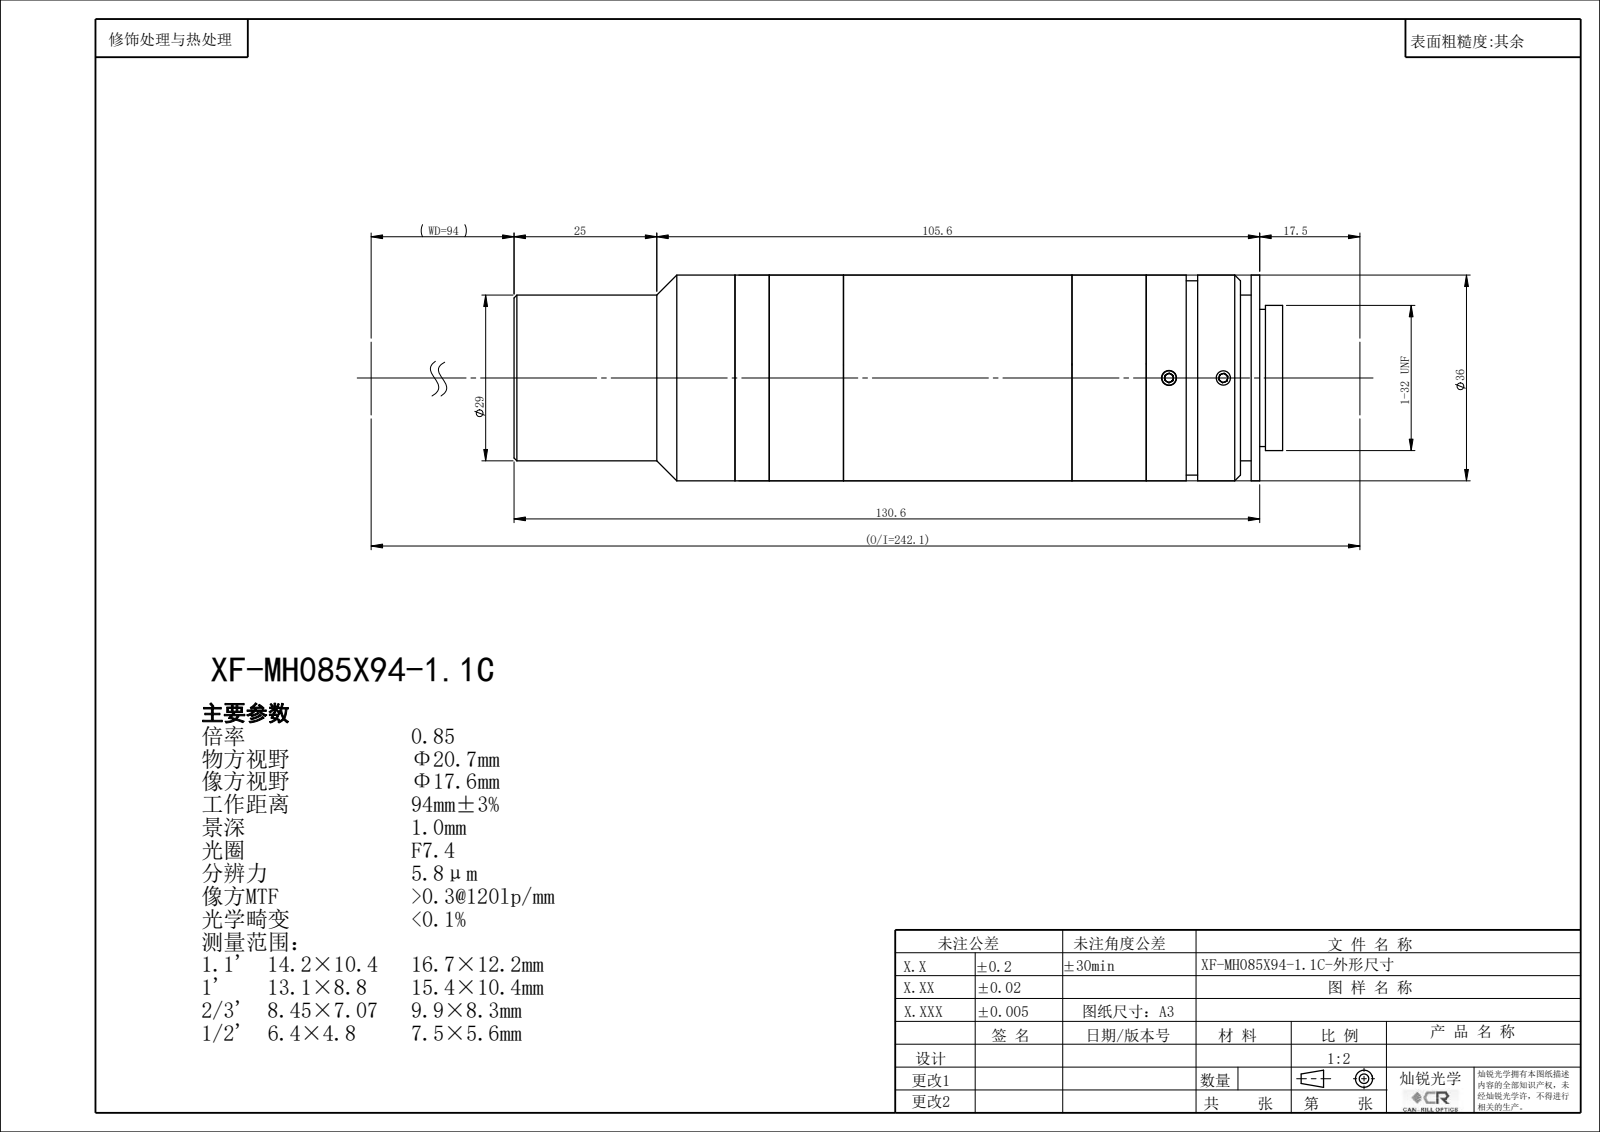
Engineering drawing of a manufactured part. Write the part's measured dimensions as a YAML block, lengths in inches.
part_name: "XF-MH085X94-1.1C"
step_written_by: "SolidWorks 2022 (CONFIG_CONTROL_DESIGN)"
units: inches
bodies: {solids: 0, faces: 140, planar: 66, cylindrical: 46, other: 28}
overall_size: [5.297, 1.417, 1.417]
round_holes:
  - {diameter: 0.098, count: 3}
  - {diameter: 0.787, count: 1}
  - {diameter: 0.882, count: 1}
  - {diameter: 0.945, count: 1}
  - {diameter: 0.98, count: 1}
  - {diameter: 1.024, count: 1}
  - {diameter: 1.039, count: 1}
round_bosses_or_shafts:
  - {diameter: 1.417, count: 1}
  - {diameter: 1.339, count: 1}
  - {diameter: 1.142, count: 1}
  - {diameter: 1, count: 1}
face_to_face_distances: [0.782, 0.059, 0.723, 0.512, 2.087, 1.235, 1.294, 1.575, 2.81, 2.869]
